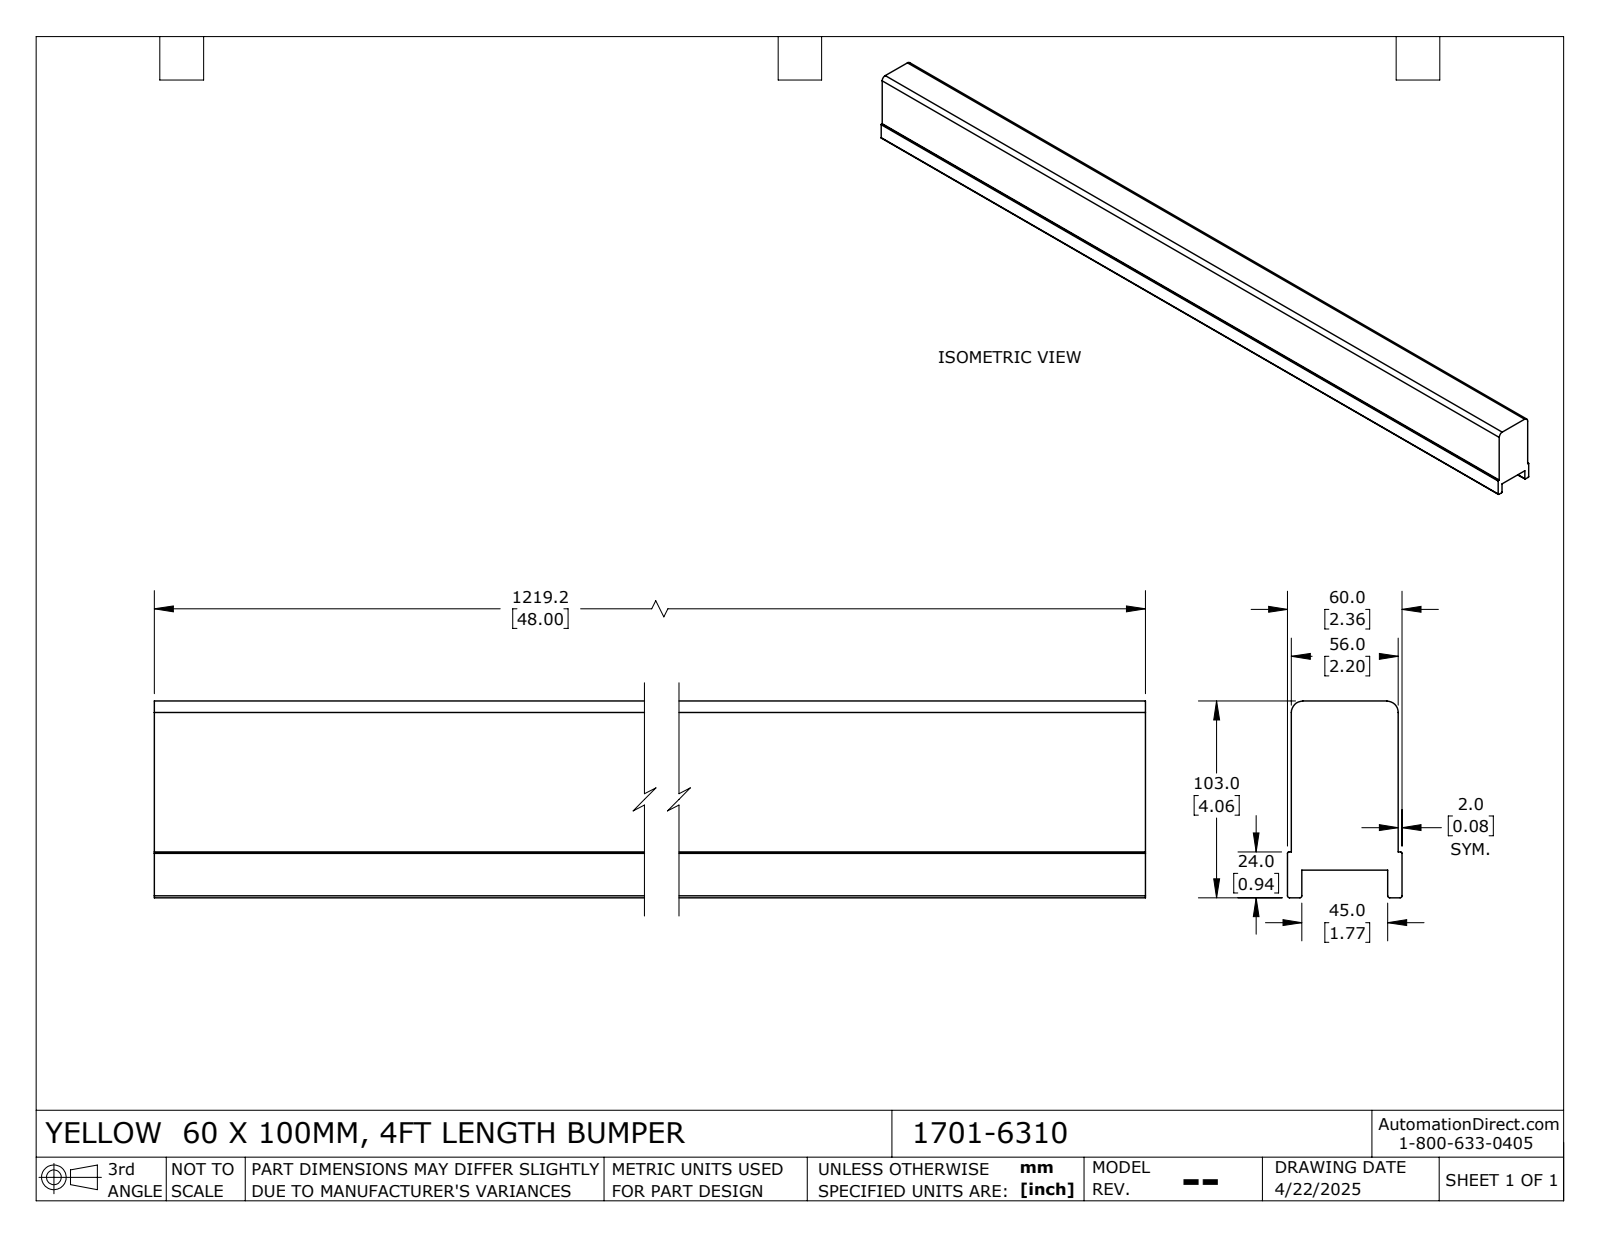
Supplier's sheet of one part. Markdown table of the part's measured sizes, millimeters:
| quantity | value |
| --- | --- |
| part name | 1701-4750_Default |
| STEP written by | SolidWorks 2021 (CONFIG_CONTROL_DESIGN) |
| units | millimeters |
| bodies | 1 solid, 22 faces (14 planar, 8 cylindrical, 0 other) |
| overall size | 1219.2 × 103 × 60 |
| volume | 6 334 000 mm³ |
| surface area | 434 100 mm² |
| partial cylindrical surfaces (radius × count) | 1 × 4, 0.8 × 2, 6 × 2 |
| main face-to-face distances | 56, 2, 58, 88.5, 7.5, 52.5, 5.5, 50.5, 60, 45 |
